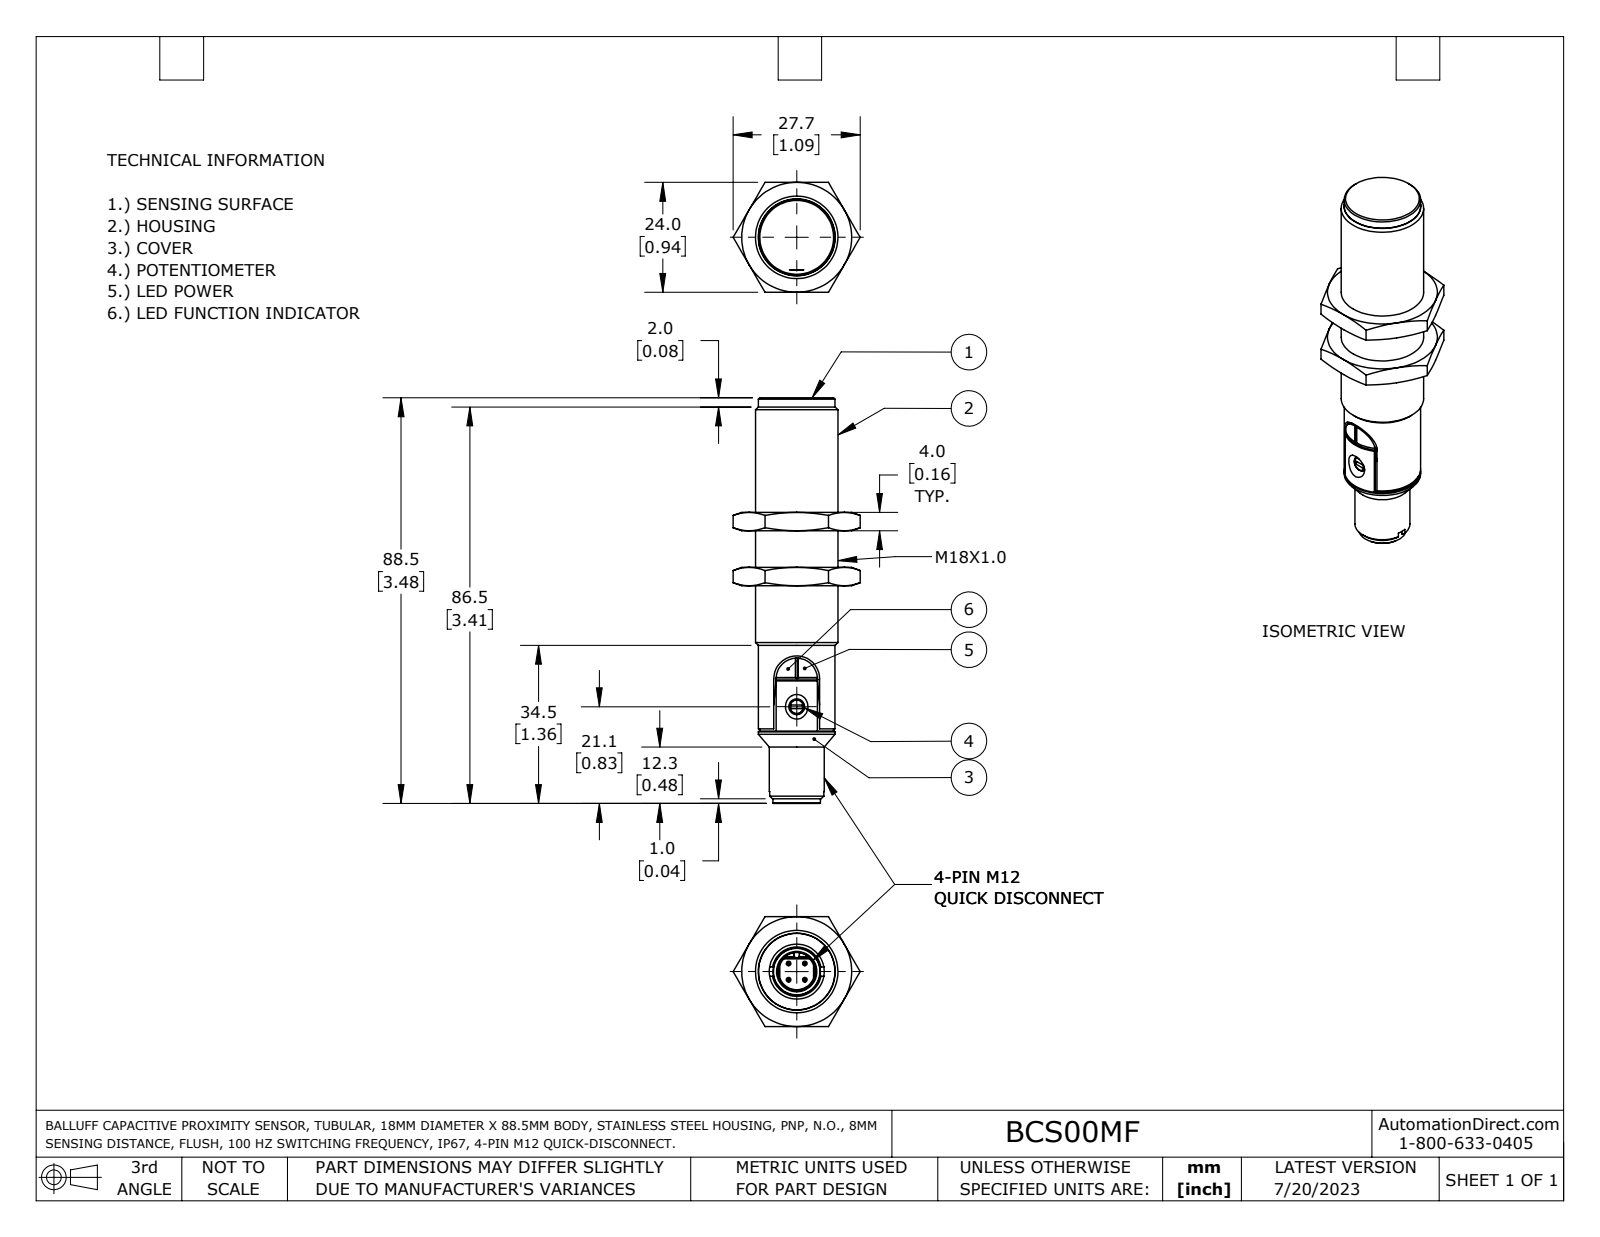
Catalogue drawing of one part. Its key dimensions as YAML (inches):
part_name: "BCS00MF"
step_written_by: "SolidWorks 2021 (AUTOMOTIVE_DESIGN)"
units: inches
bodies: {solids: 3, faces: 173, planar: 78, cylindrical: 48, other: 47}
overall_size: [3.484, 1.091, 0.945]
volume: 1.301
surface_area: 11.94
round_holes:
  - {diameter: 0.135, count: 1}
  - {diameter: 0.331, count: 1}
  - {diameter: 0.666, count: 1}
round_bosses_or_shafts:
  - {diameter: 0.039, count: 4}
  - {diameter: 0.709, count: 1}
  - {diameter: 0.657, count: 1}
  - {diameter: 0.634, count: 1}
  - {diameter: 0.472, count: 1}
  - {diameter: 0.407, count: 1}
  - {diameter: 0.123, count: 1}
partial_cylinders:
  - {radius: 0.004, count: 8}
  - {radius: 0.006, count: 2}
  - {radius: 0.009, count: 2}
  - {radius: 0.01, count: 1}
  - {radius: 0.024, count: 1}
  - {radius: 0.156, count: 1}
  - {radius: 0.164, count: 1}
  - {radius: 0.177, count: 1}
face_to_face_distances: [0.472, 0.157, 0.945, 1.142, 0.984, 1.614, 0.63, 0.315, 1.457, 1.524]
